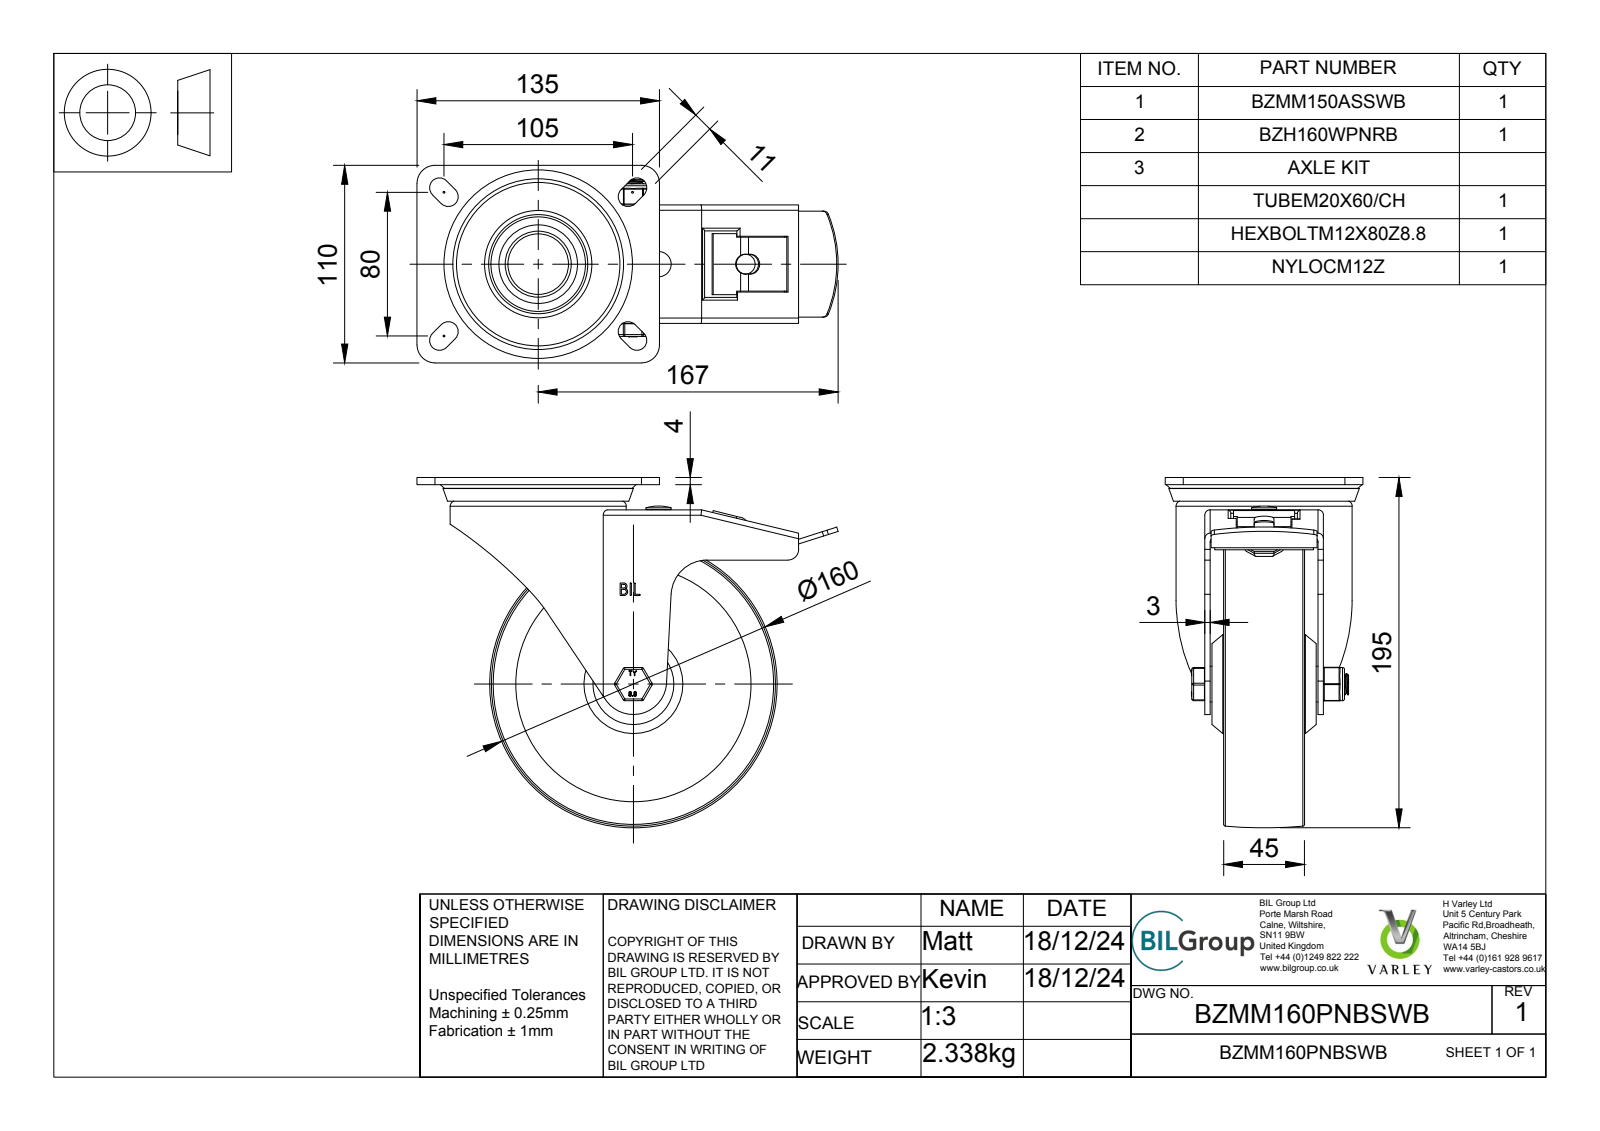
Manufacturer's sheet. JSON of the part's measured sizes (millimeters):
{"part_name": "BZMM160PNBSWB v3; BZH160WPNRB v3; NYLON CENTRE; POLYURETHANE TYRE (+7 more)", "step_written_by": "Autodesk Translation Framework v13.20.0.188 (AP242_MANAGED_MODEL_BASED_3D_ENGINEERING_MIM_LF)", "units": "millimeters", "bodies": {"solids": 66, "faces": 678, "planar": 329, "cylindrical": 212, "other": 137}, "overall_size": [234.5, 195, 110], "volume_mm3": 760273, "surface_area_mm2": 294281, "round_holes": [[8, 1], [11, 1], [12, 1], [12.2, 1], [12.5, 1], [14, 1], [20.5, 1], [30, 1], [33, 1], [33.75, 1], [39.75, 1], [92, 1]], "round_bosses_or_shafts": [[5, 10], [98, 1], [78, 1], [55, 1], [50, 1], [32.9, 1], [29.5, 1], [19.9, 1]], "partial_cylinders_radius": [[0.5, 18], [1, 12], [1.5, 10], [5.5, 10], [0.25, 6], [2.5, 6], [3, 6], [10, 4]], "face_to_face_distances": [3, 12, 9, 4, 10.5, 5, 52.5, 39, 24, 16.5], "hole_center_spacings": [67]}
